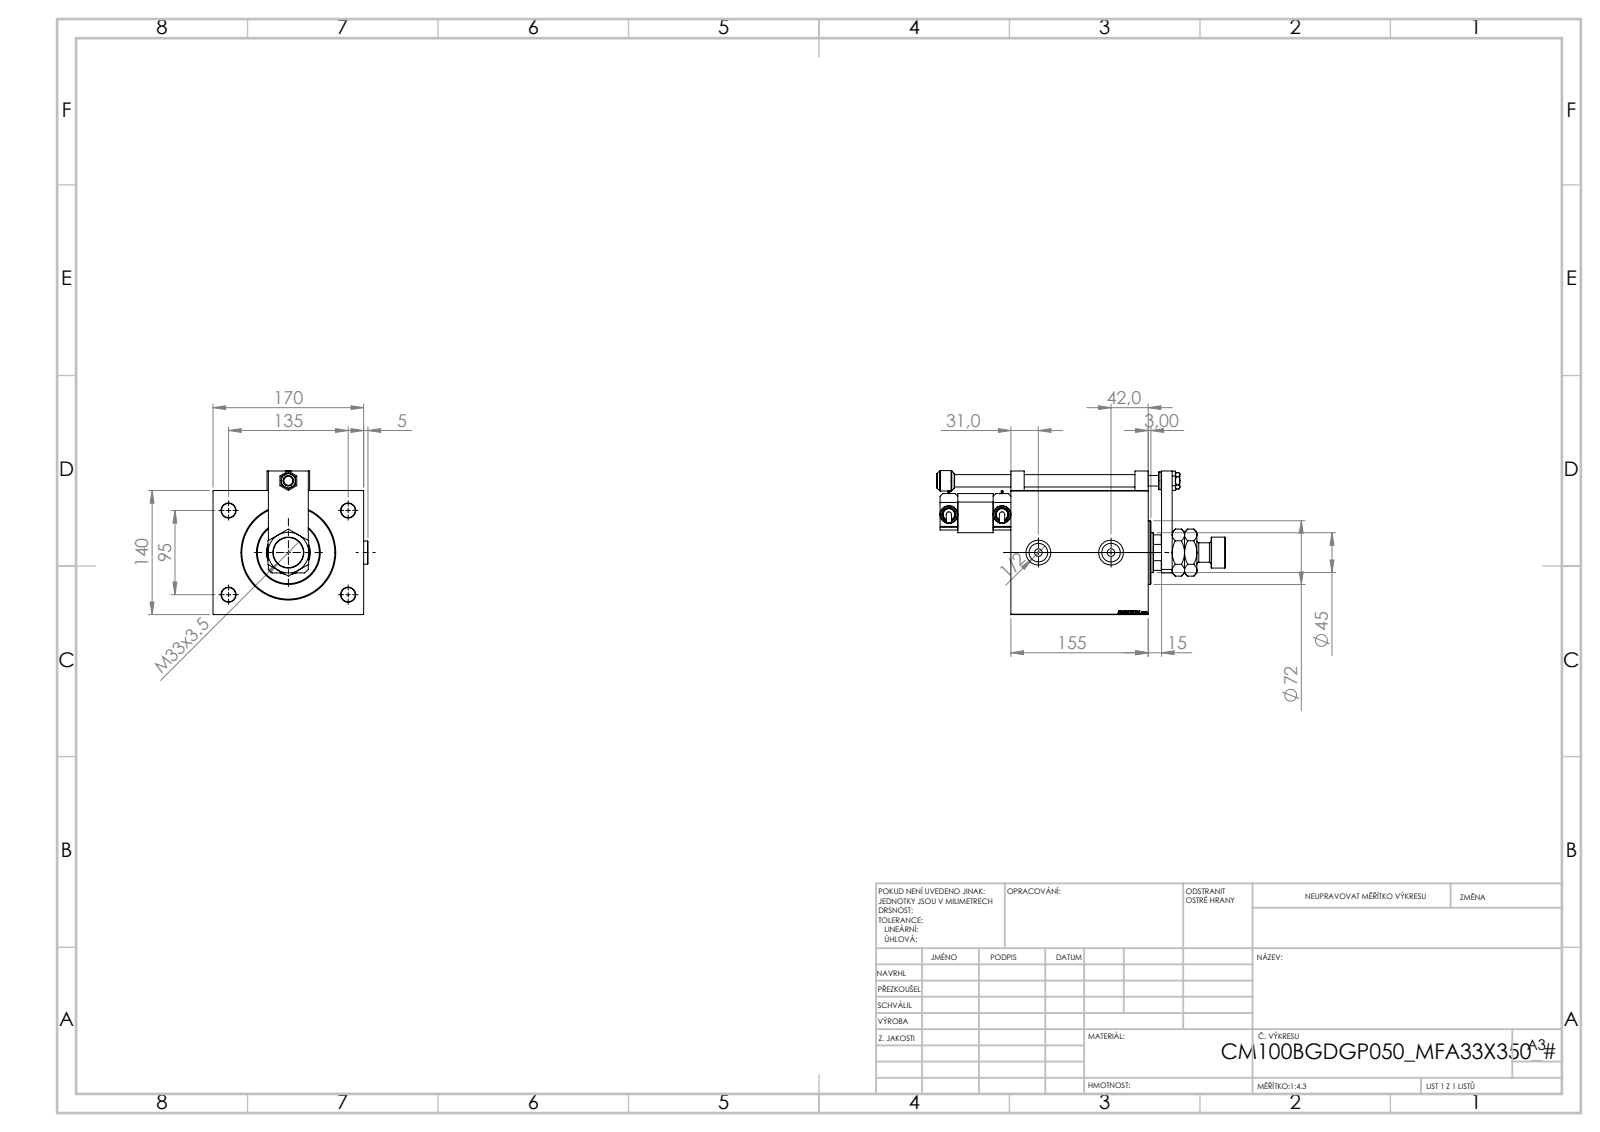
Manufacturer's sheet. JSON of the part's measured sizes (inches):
{"part_name": "Zatka_OIL_PORT; MIDDLE; P_V_Z_MFA; TYC_P (+7 more)", "step_written_by": "SolidWorks 2019 (CONFIG_CONTROL_DESIGN)", "units": "inches", "bodies": {"solids": 17, "faces": 1215, "planar": 564, "cylindrical": 134, "other": 517}, "overall_size": [12.819, 6.886, 6.398], "volume_in3": 221.5, "surface_area_in2": 548.2, "round_holes": [[0.157, 4], [0.315, 4], [0.63, 4], [0.335, 2], [0.825, 2], [1.102, 2], [0.472, 1], [0.512, 1], [0.551, 1], [1.24, 1], [1.299, 1], [1.772, 1]], "round_bosses_or_shafts": [[0.787, 3], [1.024, 2], [0.63, 2], [0.551, 2], [0.236, 2], [2.835, 1], [1.378, 1], [0.906, 1]], "partial_cylinders_radius": [[0.118, 1], [0.866, 1]], "face_to_face_distances": [5.512, 6.693, 6.102, 5.079, 1.024, 0.591, 2.559, 4.488, 3.622, 2.362], "hole_center_spacings": [3.25, 0.787, 2.967, 3.74, 5.315, 5.512, 5.568, 5.715]}
